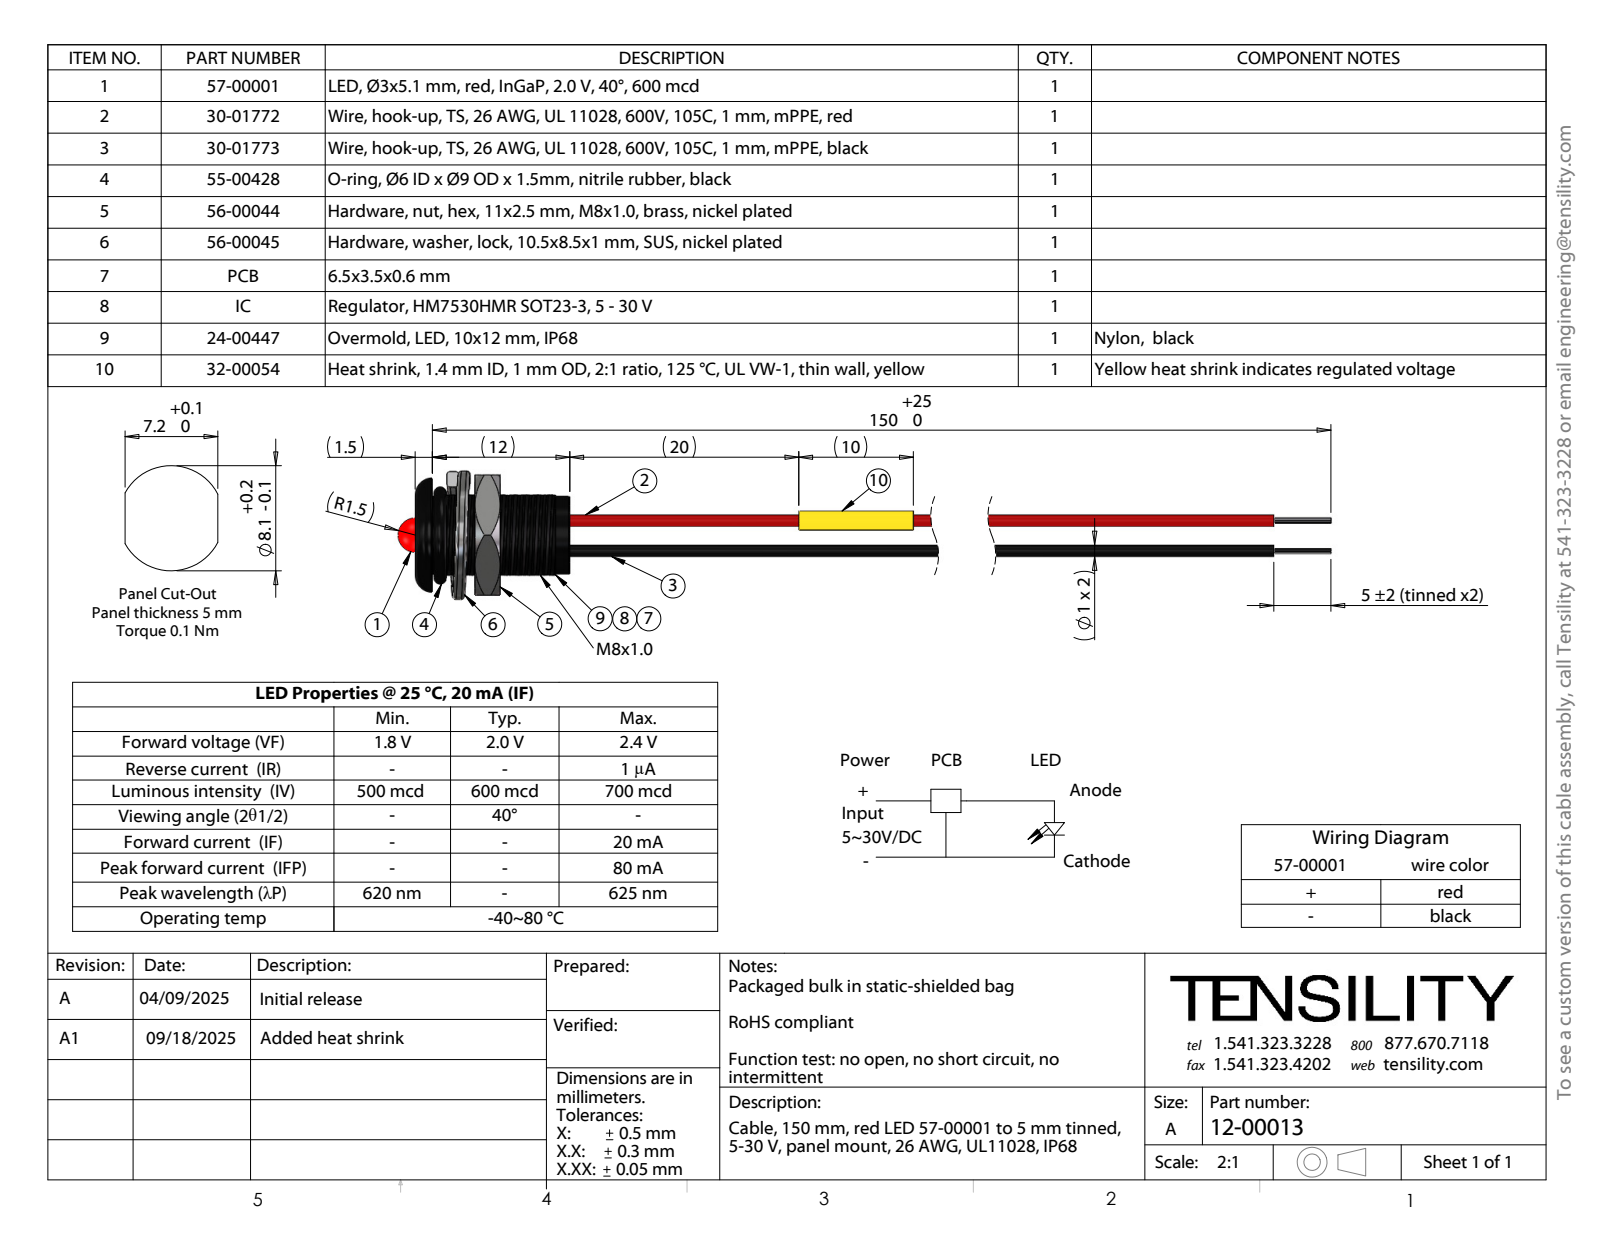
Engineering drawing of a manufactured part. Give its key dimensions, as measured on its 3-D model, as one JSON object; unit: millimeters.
{"part_name": "24-00447; 55-00428; 30-01772_stripped and tinned; 57-00001_trimmed leads (+4 more)", "step_written_by": "SolidWorks 2021 (CONFIG_CONTROL_DESIGN)", "units": "millimeters", "bodies": {"solids": 57, "faces": 555, "planar": 186, "cylindrical": 246, "other": 123}, "overall_size": [169.99, 12.12, 11.21], "volume_mm3": 1005, "surface_area_mm2": 5908, "round_holes": [[1, 2]], "round_bosses_or_shafts": [[1, 2], [0.5, 2], [6.8, 1], [3, 1]], "partial_cylinders_radius": [[3.48, 1], [4, 1]], "face_to_face_distances": [1.5, 13.5, 12, 10.5, 5.21, 3.71, 8.29, 7.41, 5.91, 2.2], "hole_center_spacings": [0.36, 0.38, 0.33, 2.48, 2.52, 2.43, 2.44, 2.56]}
